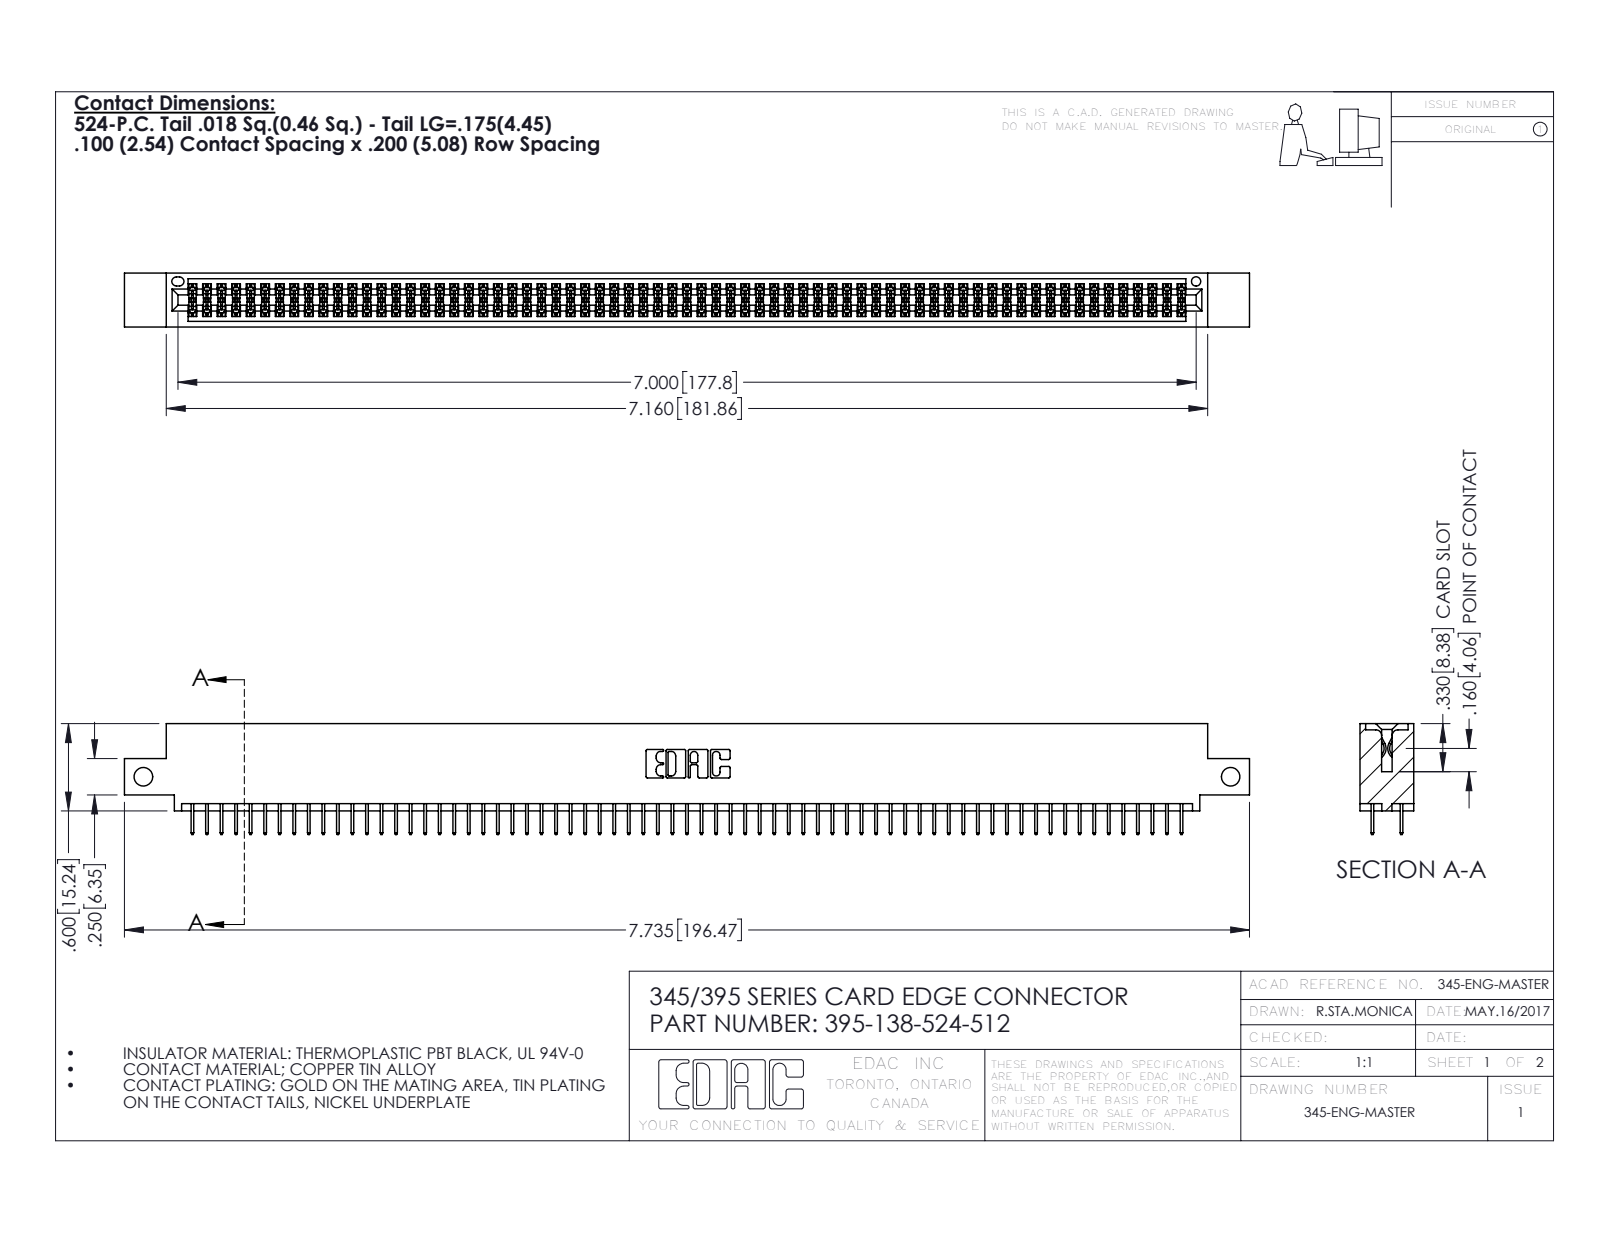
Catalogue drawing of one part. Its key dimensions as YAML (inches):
part_name: "345-292-001_345-293-124; 345 Part_0.110 Offset - Side Mount; 395-138-524-512"
step_written_by: "SolidWorks 2016 (CONFIG_CONTROL_DESIGN)"
units: inches
bodies: {solids: 139, faces: 7582, planar: 5466, cylindrical: 2116, other: 0}
overall_size: [7.735, 0.762, 0.37]
volume: 1.157
surface_area: 43.34
round_holes:
  - {diameter: 0.128, count: 2}
  - {diameter: 0.064, count: 1}
partial_cylinders:
  - {radius: 0.006, count: 207}
  - {radius: 0.01, count: 22}
  - {radius: 0.007, count: 6}
  - {radius: 0.031, count: 6}
  - {radius: 0.026, count: 3}
  - {radius: 0.014, count: 2}
  - {radius: 0.019, count: 2}
  - {radius: 0.022, count: 2}
face_to_face_distances: [0.072, 0.298, 0.2, 0.37, 0.098, 0.272, 0.025, 0.225, 0.072, 0.175]
hole_center_spacings: [7.475]
